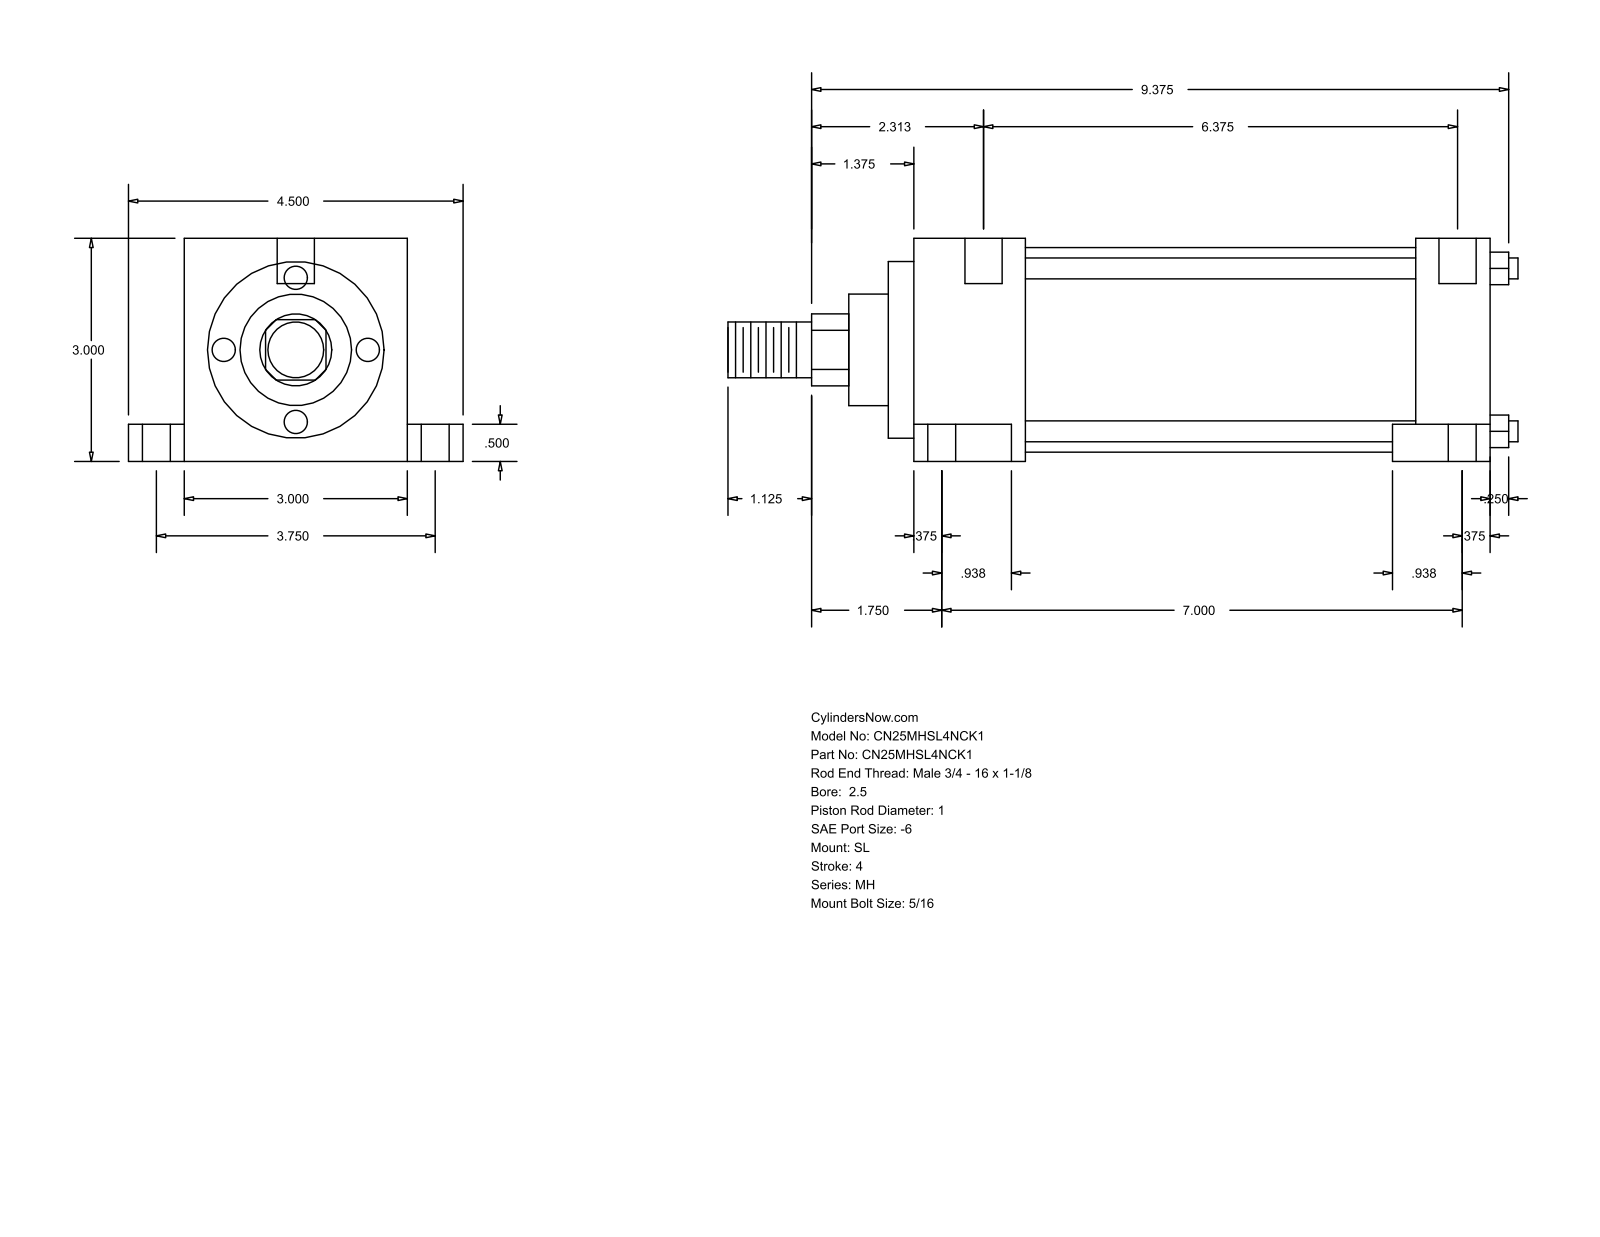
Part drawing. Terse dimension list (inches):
name: MH_SL__0250_1
written by: GSSL Pune (CONFIG_CONTROL_DESIGN)
unit: in
bodies: 0 solids, 86 faces (61 planar, 25 cylindrical, 0 other)
size: 10.625 × 4.5 × 3
holes: 2× ⌀0.219, 2× ⌀0.375, 2× ⌀0.625, 1× ⌀0.5
bosses: 4× ⌀0.281, 1× ⌀2.75, 1× ⌀2.375, 1× ⌀1.5, 1× ⌀1, 1× ⌀0.75
rounds: 1× R0.484
face distances: 3, 1, 7.094, 8.094, 0.5, 2.5, 0.75, 3.75, 0.531, 7.625
hole spacings: 1.876, 0.125, 3.75
